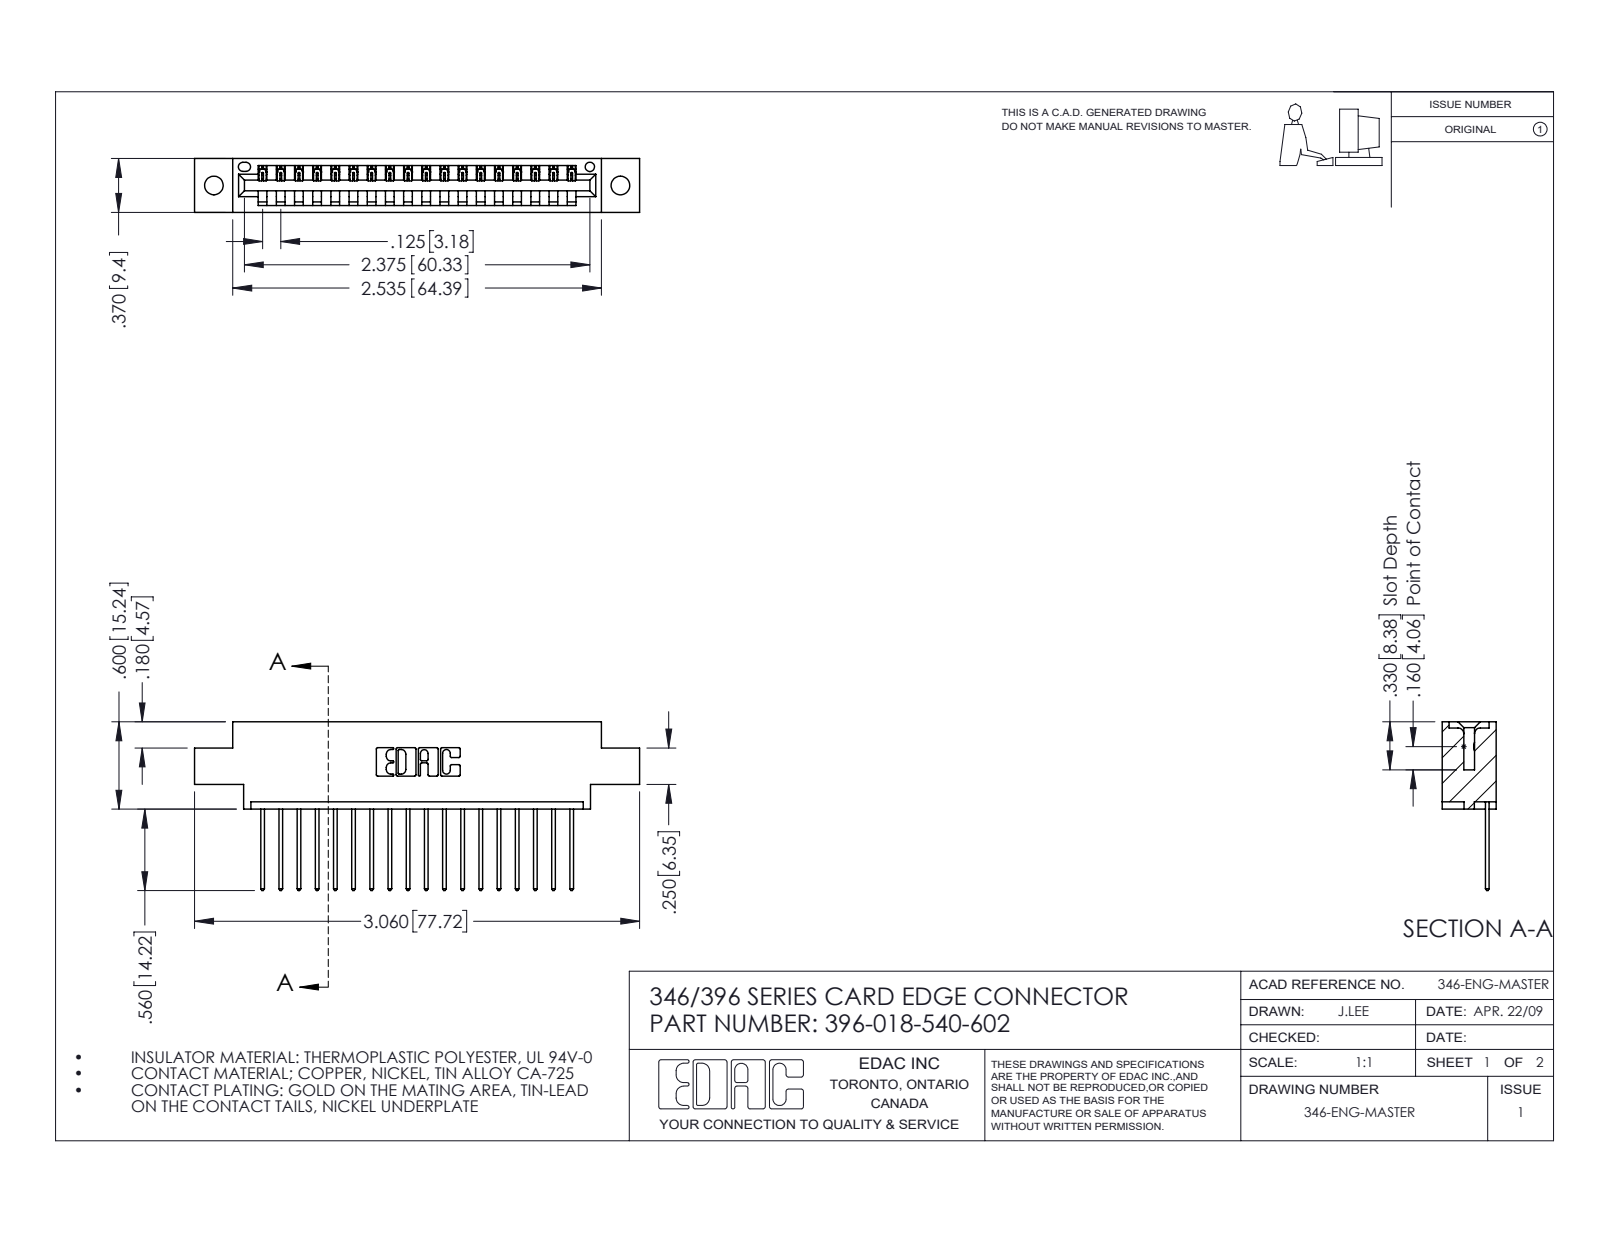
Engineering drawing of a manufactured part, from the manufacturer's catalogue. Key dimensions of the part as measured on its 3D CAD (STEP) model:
Part name (STEP PRODUCT): 345-292-001_345-293-140; 346 Part_0.170 Offset - 0.128 Dia; 396-018-540-602
STEP written by: SolidWorks 2016 (CONFIG_CONTROL_DESIGN)
Units: inches
Bodies: 19 solids, 1170 faces (800 planar, 370 cylindrical, 0 other)
Overall size (bounding box): 3.06 × 1.16 × 0.37
Volume: 0.434 in³ · Surface area: 13.47 in²
Round holes (diameter × count): ⌀0.128 ×2, ⌀0.064 ×1
Partial cylindrical surfaces — rounded edges, fillets, slot ends (radius × count): R0.006 ×36, R0.01 ×36, R0.01 ×22, R0.007 ×6, R0.031 ×6, R0.026 ×3, R0.031 ×2, R0.04 ×2
Main face-to-face distances: 0.048, 0.322, 0.37, 0.25, 0.072, 0.298, 0.025, 0.148, 0.222, 0.1
Hole centre spacings: 0.246, 2.588, 2.795
